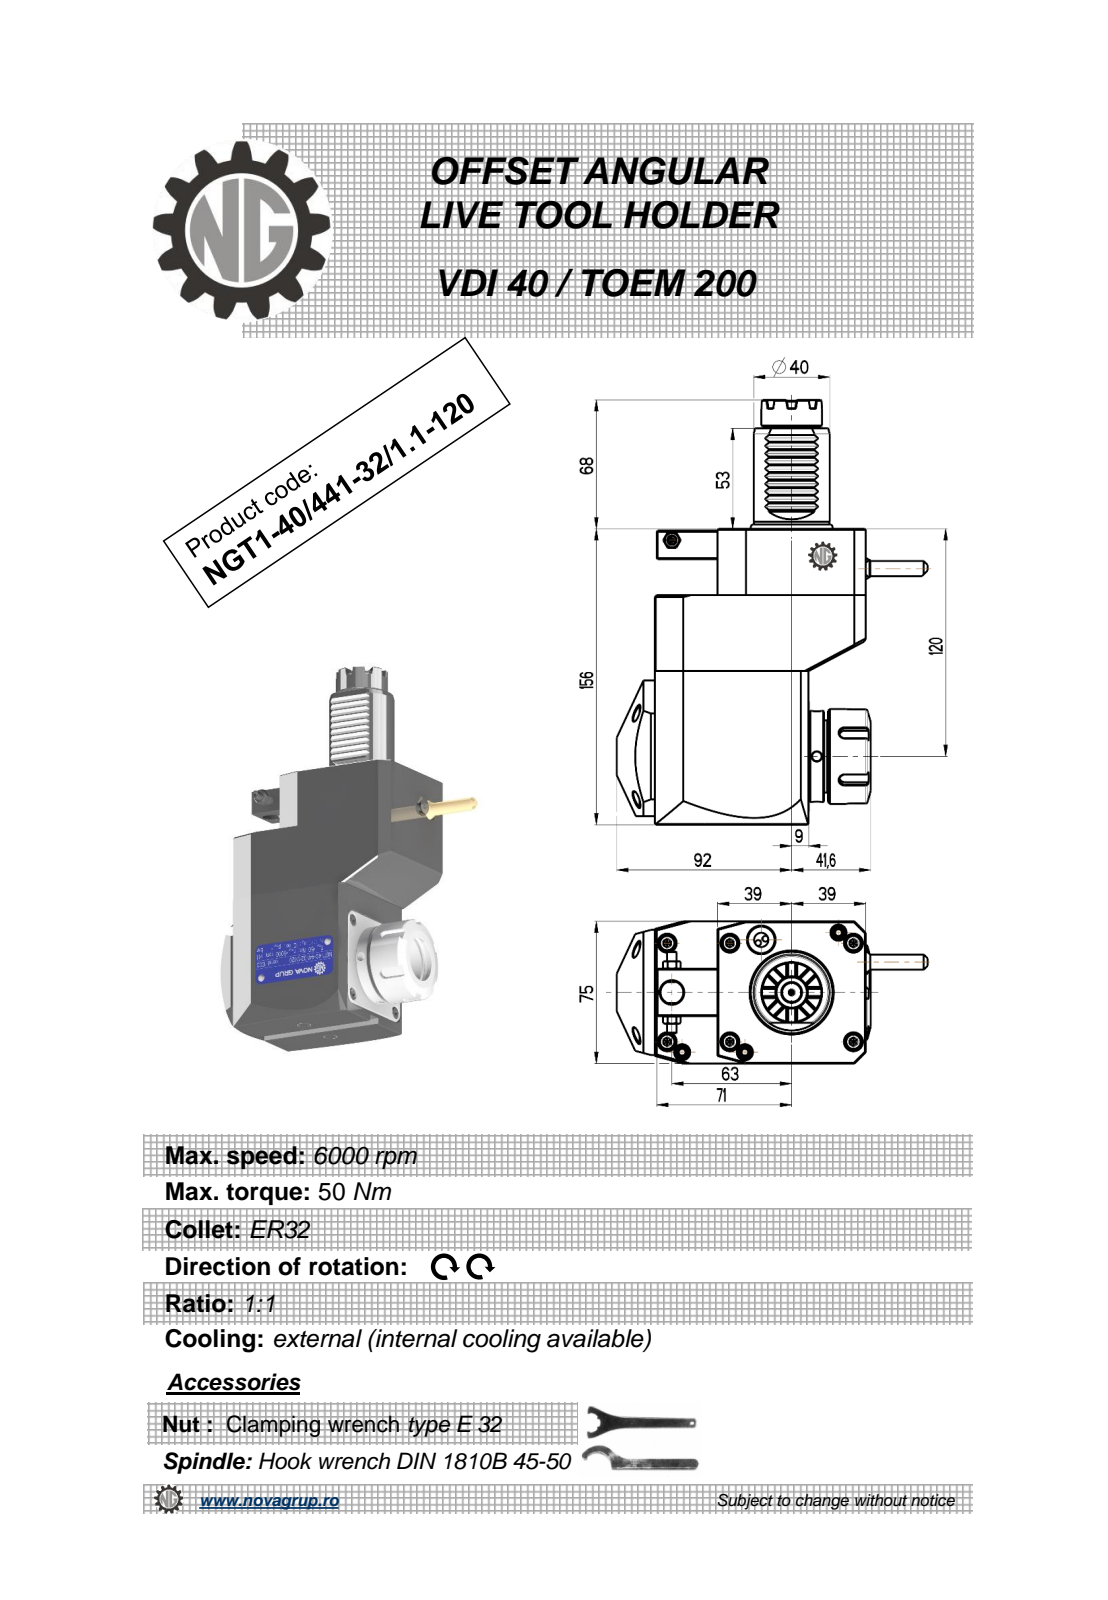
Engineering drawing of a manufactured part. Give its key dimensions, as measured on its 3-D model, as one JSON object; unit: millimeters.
{"part_name": "NGT1_40_441_32_1_1_120", "step_written_by": "PRO/ENGINEER BY PARAMETRIC TECHNOLOGY CORPORATION, 2010280 (CONFIG_CONTROL_DESIGN)", "units": "millimeters", "bodies": {"solids": 1, "faces": 500, "planar": 239, "cylindrical": 94, "other": 167}, "overall_size": [224, 163.5, 76.6], "volume_mm3": 1189000, "surface_area_mm2": 88888, "round_holes": [[5, 3], [3, 1], [9.5, 1], [12, 1], [27, 1]], "round_bosses_or_shafts": [[50, 1], [48, 1], [41, 1], [40, 1], [32, 1], [17, 1], [10, 1], [8.96, 1]], "partial_cylinders_radius": [[0.26, 12], [0.3, 10], [0.2, 6], [3, 5], [0.5, 1], [8.6, 1], [40, 1]], "face_to_face_distances": [75, 156, 111, 35, 121, 30, 81, 33, 78, 48], "hole_center_spacings": [20.93, 76.25, 100.28, 112.5]}
